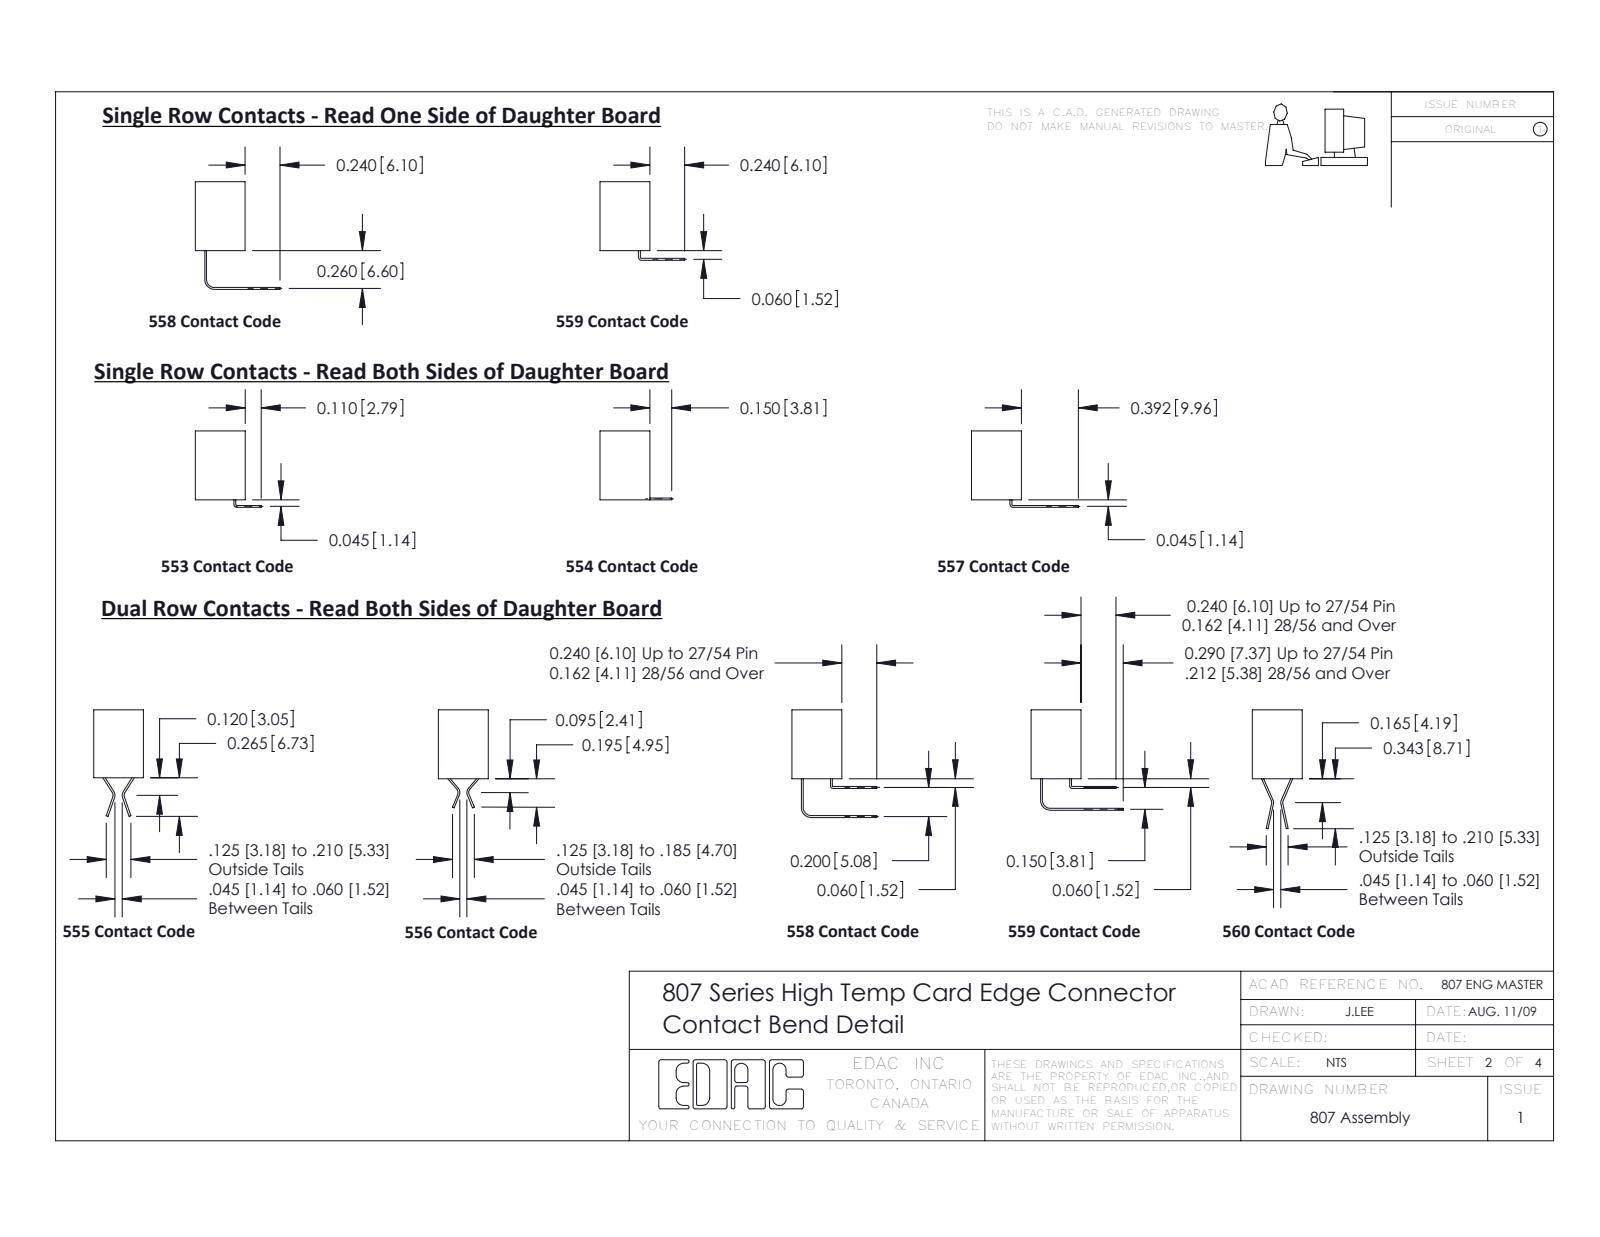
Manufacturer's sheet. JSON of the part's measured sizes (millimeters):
{"part_name": "345-250-001_345-250-001-102; 307-220-078; 307 Part_.156 Dia Mounting Holes; 307-086-540-278 (+1 more)", "step_written_by": "SolidWorks 2016 (CONFIG_CONTROL_DESIGN)", "units": "millimeters", "bodies": {"solids": 78, "faces": 3780, "planar": 2495, "cylindrical": 1181, "other": 104}, "overall_size": [193.4, 63.7, 12.7], "volume_mm3": 24810, "surface_area_mm2": 30640, "round_holes": [[2.3, 2], [3.2, 2], [4, 2]], "round_bosses_or_shafts": [[3.9, 2]], "partial_cylinders_radius": [[0.5, 208], [0.6, 38], [0.3, 22], [0.8, 8], [0.2, 6], [0.8, 6], [0.7, 3], [0.3, 2]], "face_to_face_distances": [8.7, 9.1, 5.1, 3.6, 4, 0.3, 10.7, 0.4, 2, 3.6], "hole_center_spacings": [185.5]}
